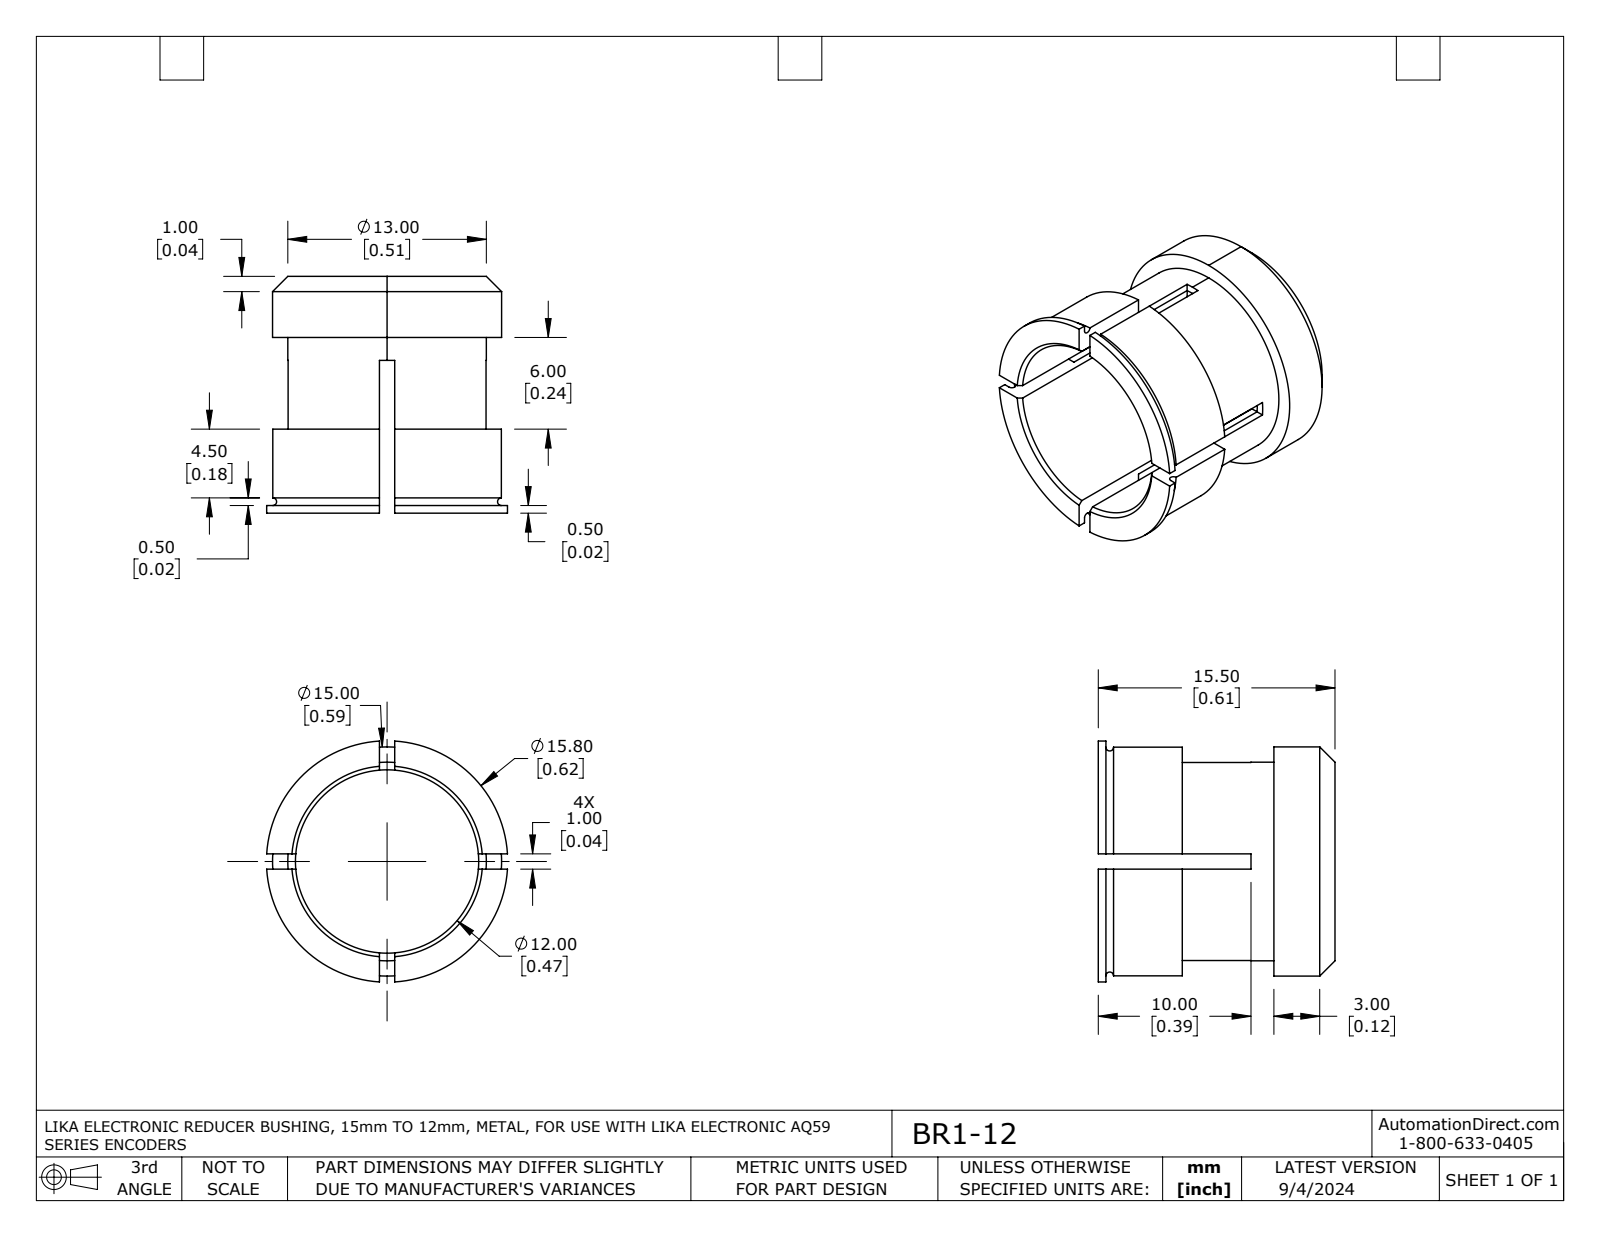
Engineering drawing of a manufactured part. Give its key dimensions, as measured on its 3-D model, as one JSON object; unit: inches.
{"part_name": "BR1-12", "step_written_by": "SolidWorks 2021 (AUTOMOTIVE_DESIGN)", "units": "inches", "bodies": {"solids": 1, "faces": 54, "planar": 26, "cylindrical": 17, "other": 11}, "overall_size": [0.621, 0.621, 0.61], "volume_in3": 0.04, "surface_area_in2": 2.33, "round_holes": [[0.472, 1]], "round_bosses_or_shafts": [[0.622, 1], [0.591, 1], [0.512, 1]], "face_to_face_distances": [0.453, 0.039, 0.217, 0.236, 0.394, 0.157, 0.61, 0.591, 0.433, 0.197]}
